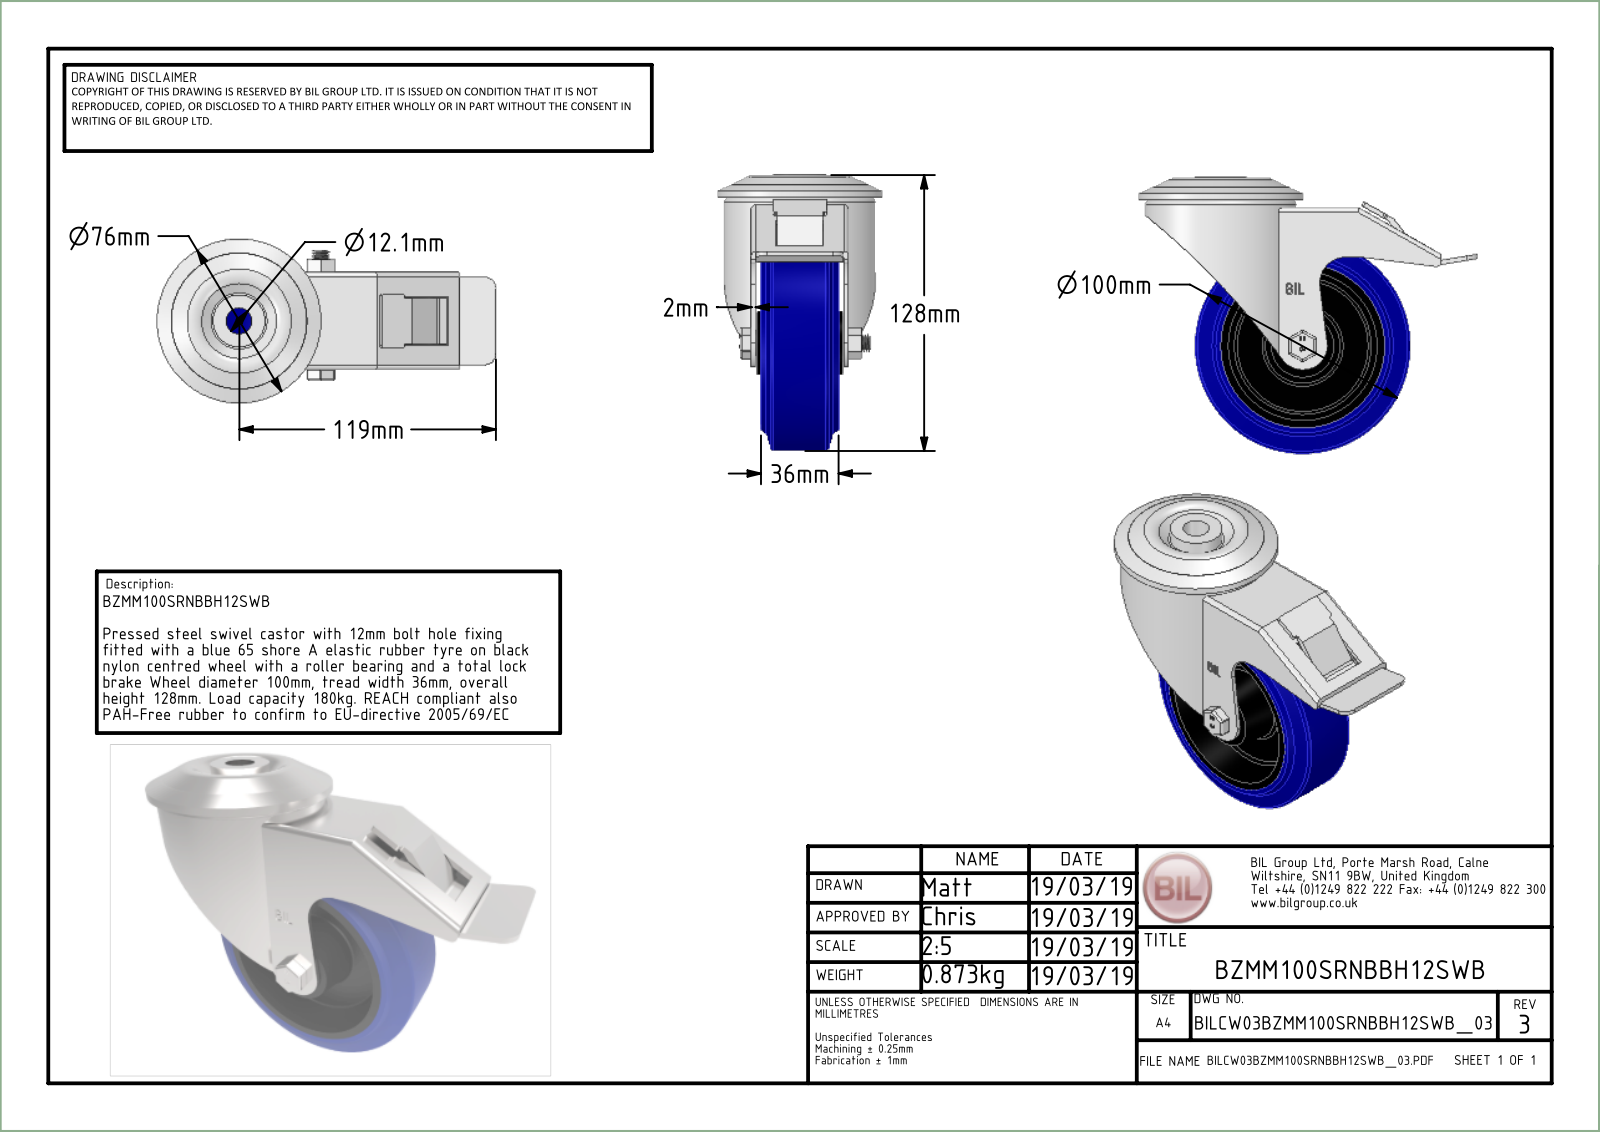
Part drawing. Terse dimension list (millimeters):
name: BZMM100SRNBBH12SWB v3; BZMM100ASBH12SWB v1; PRESSED STEEL, ZINC PLATED HEAD; PRESSED STEEL, ZINC PLATED FORKS (+8 more)
written by: Autodesk Translation Framework v13.20.0.188 (AUTOMOTIVE_DESIGN)
unit: mm
bodies: 20 solids, 675 faces (343 planar, 228 cylindrical, 104 other)
size: 157 × 128 × 76
volume: 256 727 mm³; area: 127 352 mm²
holes: 2× ⌀0.66, 1× ⌀8, 1× ⌀8.2, 1× ⌀8.4, 1× ⌀8.6, 1× ⌀12.2, 1× ⌀12.5, 1× ⌀13, 1× ⌀20.5, 1× ⌀25, 1× ⌀65, 1× ⌀72
bosses: 8× ⌀3.75, 1× ⌀70, 1× ⌀49.5, 1× ⌀38, 1× ⌀30.5, 1× ⌀24.9, 1× ⌀24, 1× ⌀21.31
rounds: 50× R0.75, 18× R0.5, 12× R0.25, 10× R1.25, 4× R0.33, 4× R0.64, 4× R2.5, 3× R2
face distances: 2.5, 42.5, 17, 19.5, 25.5, 23, 4.5, 2, 40, 15
hole spacings: 3.22, 2.49
